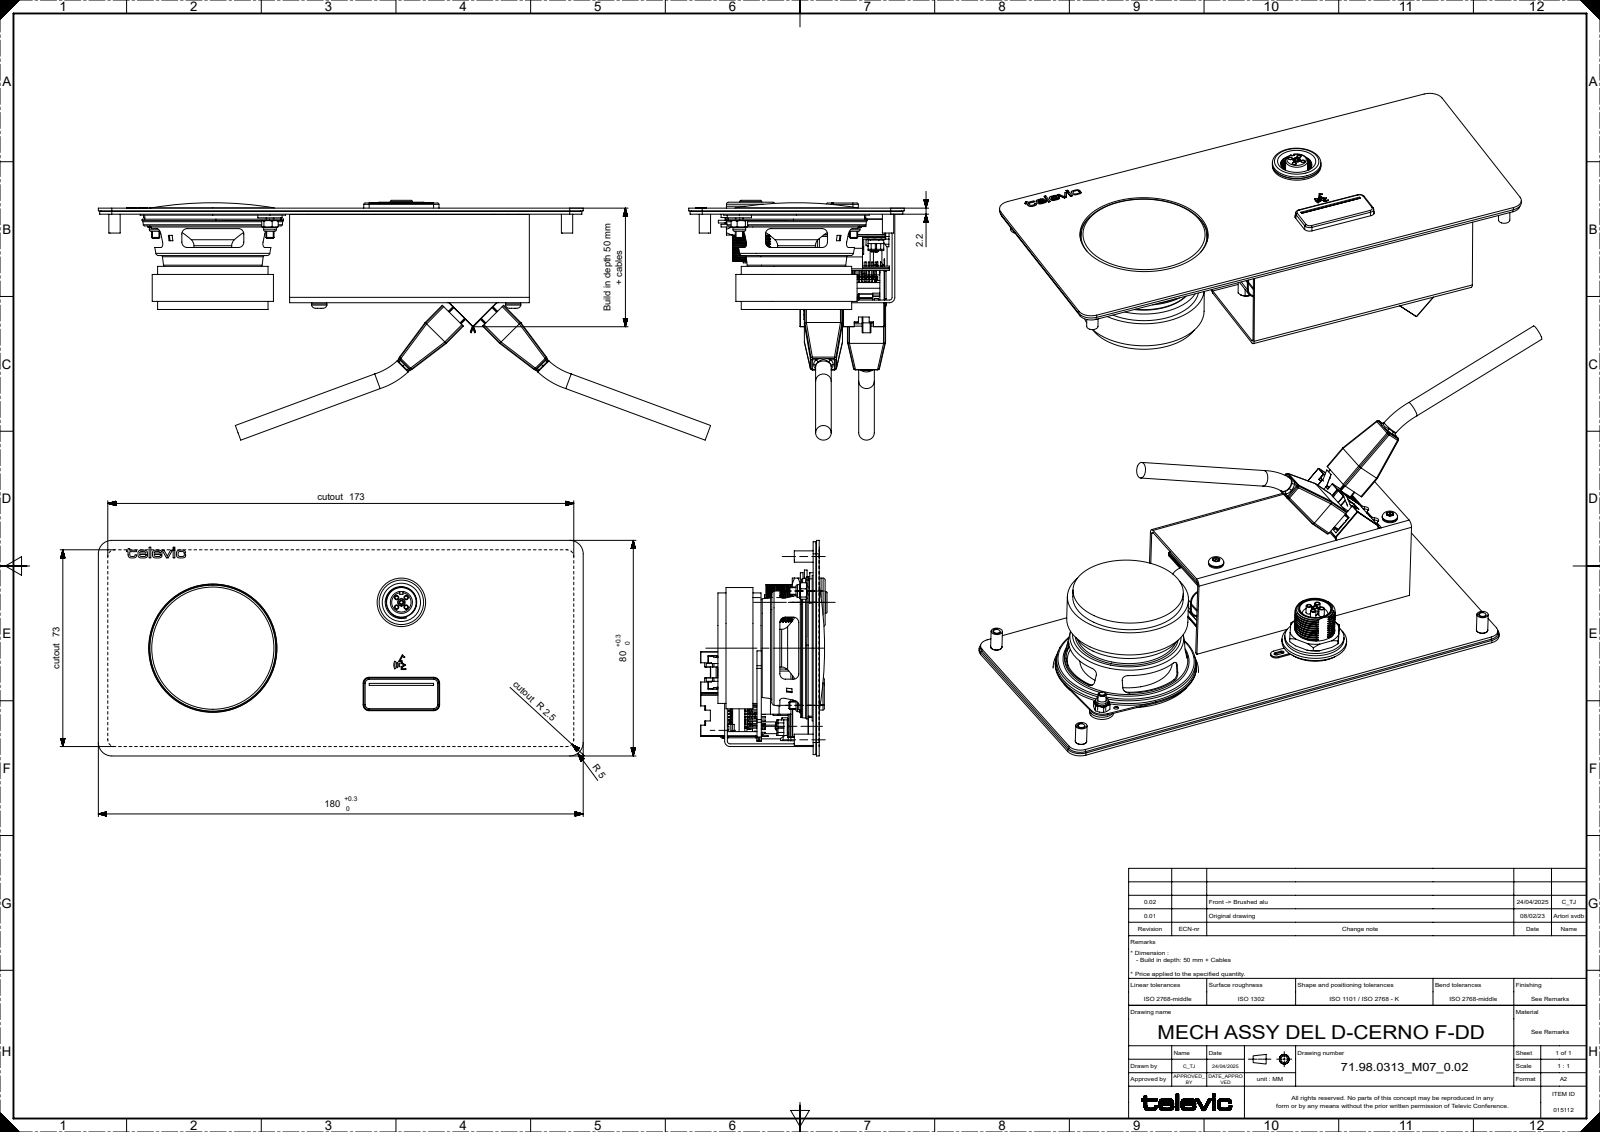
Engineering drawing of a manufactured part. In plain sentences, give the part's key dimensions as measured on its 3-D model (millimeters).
The part is named "000080_0.04-05.35.9001; 000078_0.04-05.35.9001; 000081_0.04-05.35.9001; 3500015_VC-3500015 (+8 more)". Its 3-D file was written by "SIEMENS PLM Software NX 2000 (AUTOMOTIVE_DESIGN)". It is 93 solids with 4180 faces: 2285 planar, 1076 cylindrical and 819 other. Overall it measures 245.48 by 88.98 by 80 millimeters. Its volume is 122 581 cubic millimeters and its surface area 195 137 square millimeters. Round holes: 6 of diameter 2.44, 6 of diameter 2.46, 6 of diameter 3.5, 6 of diameter 4.25, 5 of diameter 1.4, 5 of diameter 3.2, 4 of diameter 3.35, 2 of diameter 1.8, 2 of diameter 4.2, 2 of diameter 6, 1 of diameter 2.8, 1 of diameter 9.7. Round bosses or shafts: 6 of diameter 4.2, 6 of diameter 3.7, 6 of diameter 3, 6 of diameter 2.5, 5 of diameter 2, 4 of diameter 5.8, 4 of diameter 4.6, 4 of diameter 3.3. Partial cylindrical surfaces (rounded edges, fillets, slot ends): 182 of radius 0.25, 66 of radius 0.5, 60 of radius 0.2, 56 of radius 1, 26 of radius 0.75, 16 of radius 2.5, 15 of radius 2, 12 of radius 1.95. The main face-to-face distances are 1, 1.25, 11.6, 0.6, 20.5, 1.6, 2.25, 20.85, 22.1, 21.5. The hole center spacings are 2.5, 3.54, 5.01, 5.38, 28.44, 30, 49.88, 58.2.
